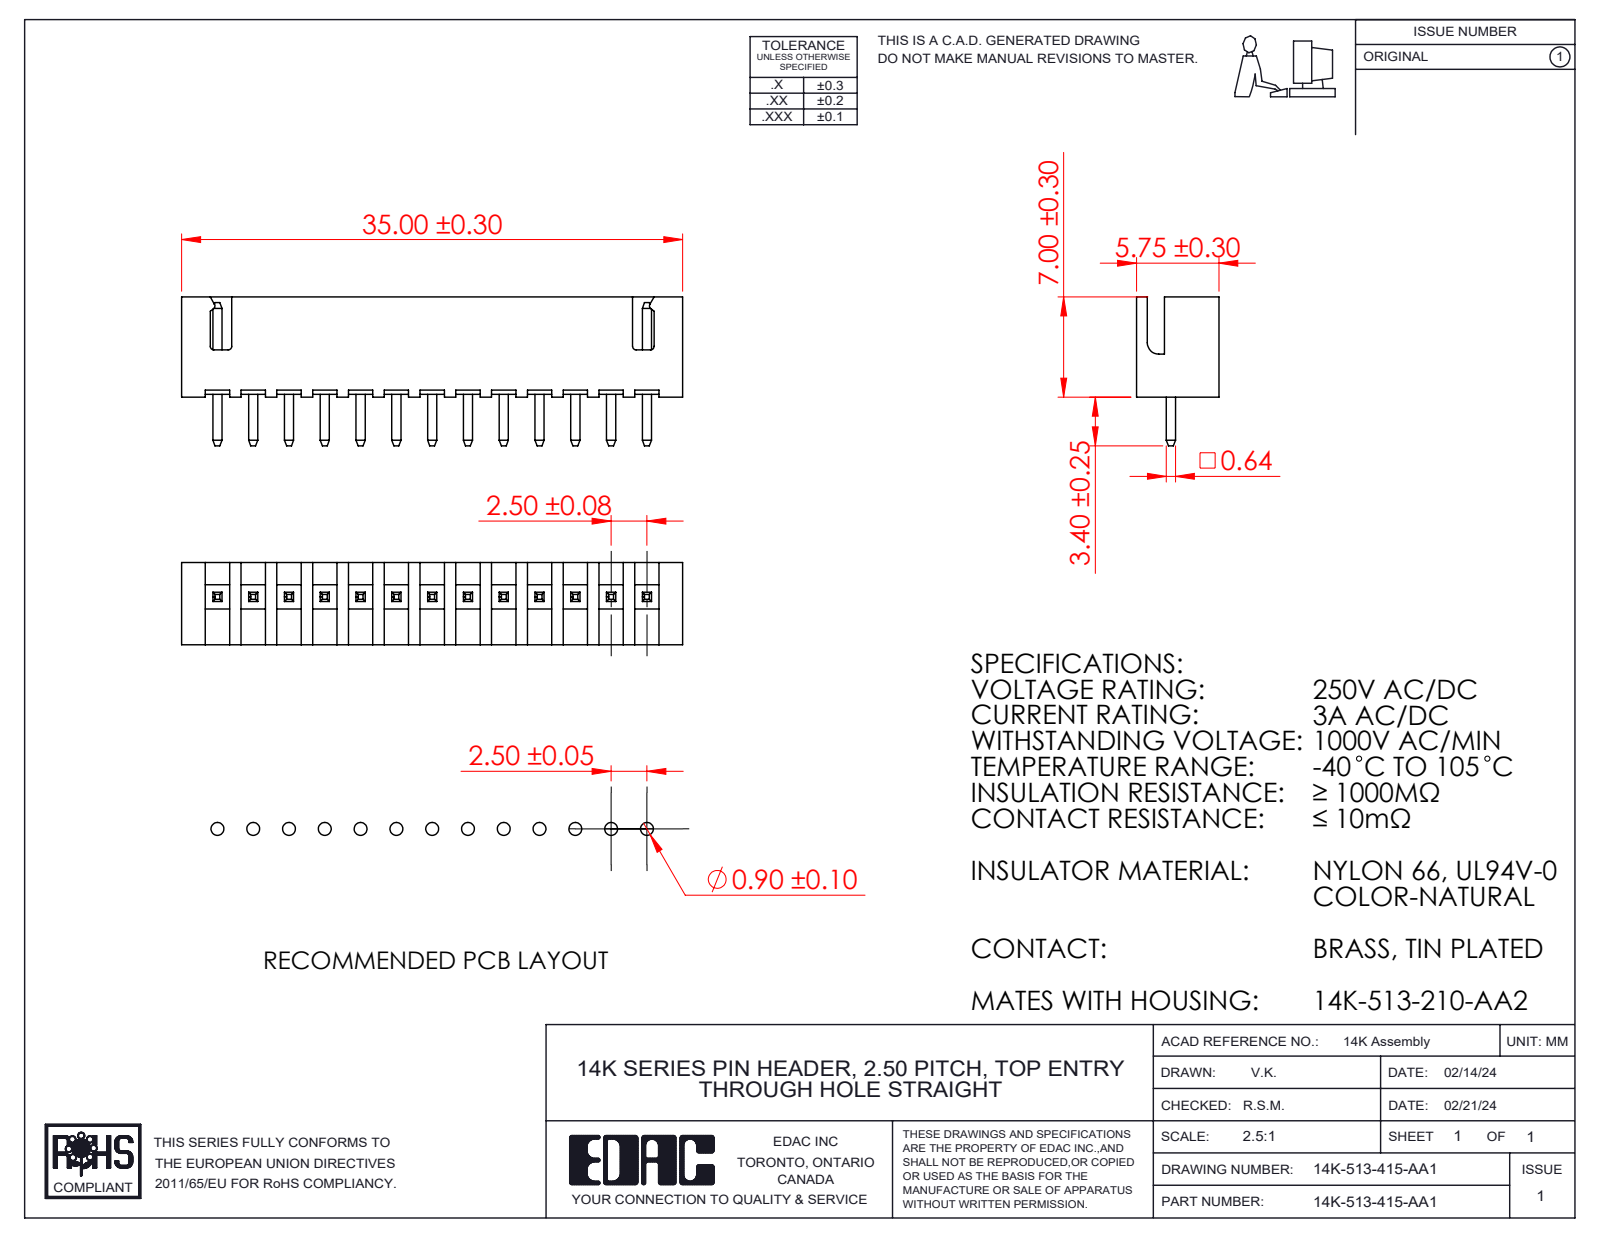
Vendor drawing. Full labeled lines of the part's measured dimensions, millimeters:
Part name (STEP PRODUCT): 14K Series Pin_15; 14K Series Pin Header Insulator_513; 14K-513-415-AA1
STEP written by: SolidWorks 2023 (CONFIG_CONTROL_DESIGN)
Units: millimetres
Bodies: 14 solids, 378 faces (369 planar, 9 cylindrical, 0 other)
Overall size (bounding box): 35 × 10.4 × 5.75
Volume: 647 mm³ · Surface area: 1 761 mm²
Partial cylindrical surfaces — rounded edges, fillets, slot ends (radius × count): R0.25 ×6, R0.8 ×1
Main face-to-face distances: 5, 0.76, 5.76, 4.24, 0.64, 3.04, 2.28, 1.96, 2.72, 2.5
